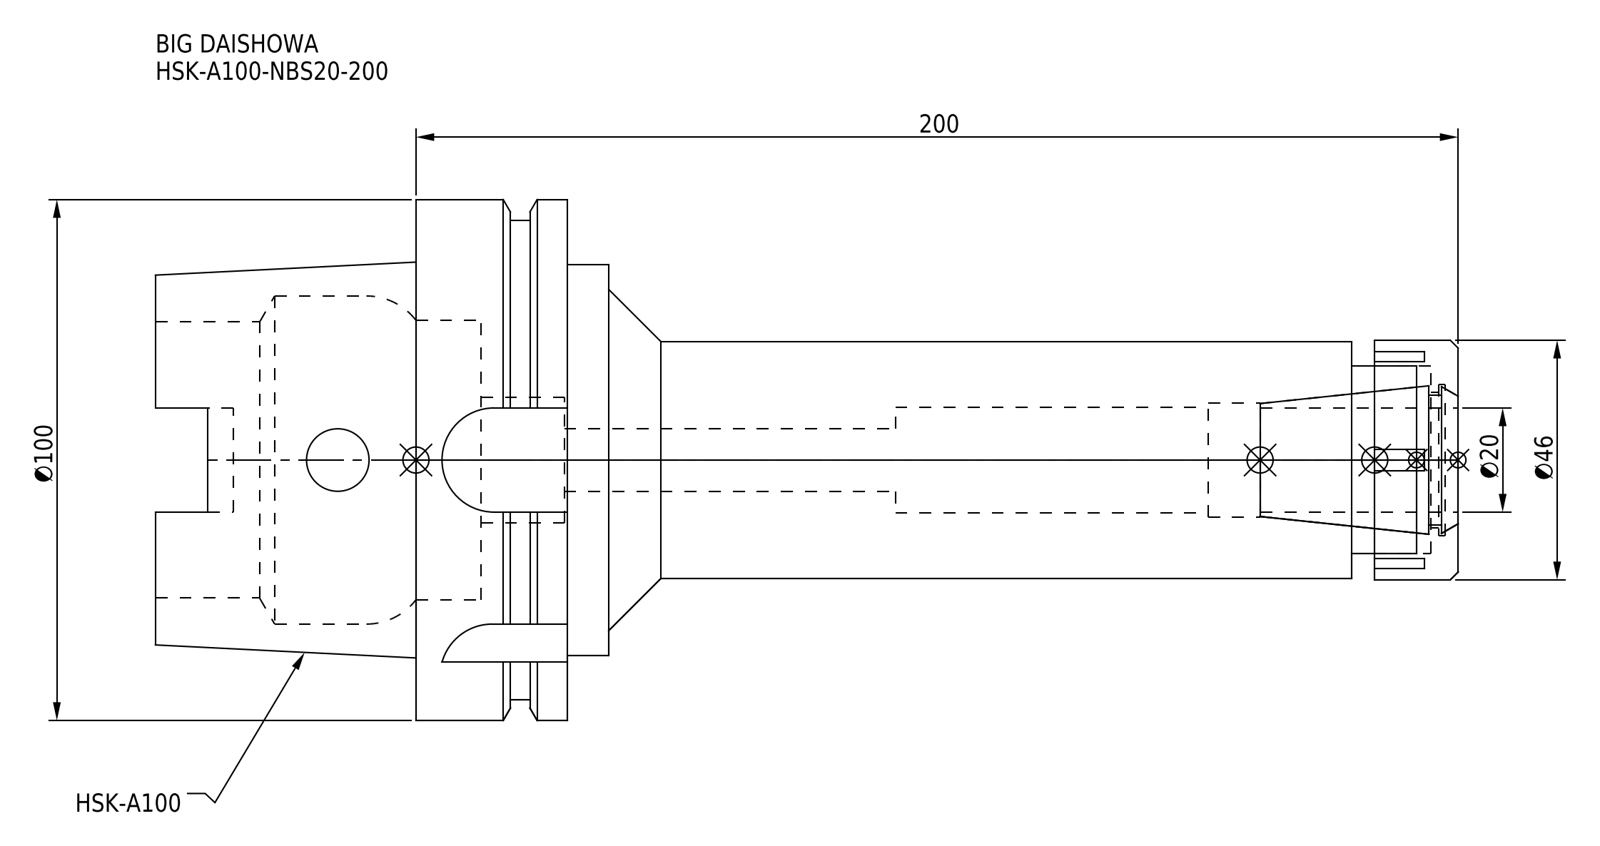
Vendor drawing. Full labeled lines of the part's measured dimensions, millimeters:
Part name (STEP PRODUCT): NBN20_1.stp; HSK-A100-NBS20-200-FreeParts; HSK-A100-NBS20-200.stp; HSK-A100-NBS20-200_1.stp (+3 more)
STEP written by: SolidWorks 2019 (CONFIG_CONTROL_DESIGN)
Units: millimetres
Bodies: 2 solids, 138 faces (66 planar, 50 cylindrical, 22 other)
Overall size (bounding box): 250 × 100 × 100
Volume: 508 353 mm³ · Surface area: 88 505 mm²
Round holes (diameter × count): ⌀12 ×2, ⌀20.3 ×1, ⌀22 ×1, ⌀24 ×1, ⌀26 ×1, ⌀29 ×1, ⌀36 ×1, ⌀53 ×1, ⌀53.8 ×1, ⌀63 ×1
Round bosses / shafts (diameter × count): ⌀100 ×1, ⌀92 ×1, ⌀75 ×1, ⌀46 ×1, ⌀45.5 ×1
Partial cylindrical surfaces — rounded edges, fillets, slot ends (radius × count): R4.88 ×4, R10 ×4
Main face-to-face distances: 29, 8, 16.55, 12.45, 163, 24.55, 37, 87, 79, 62.45
